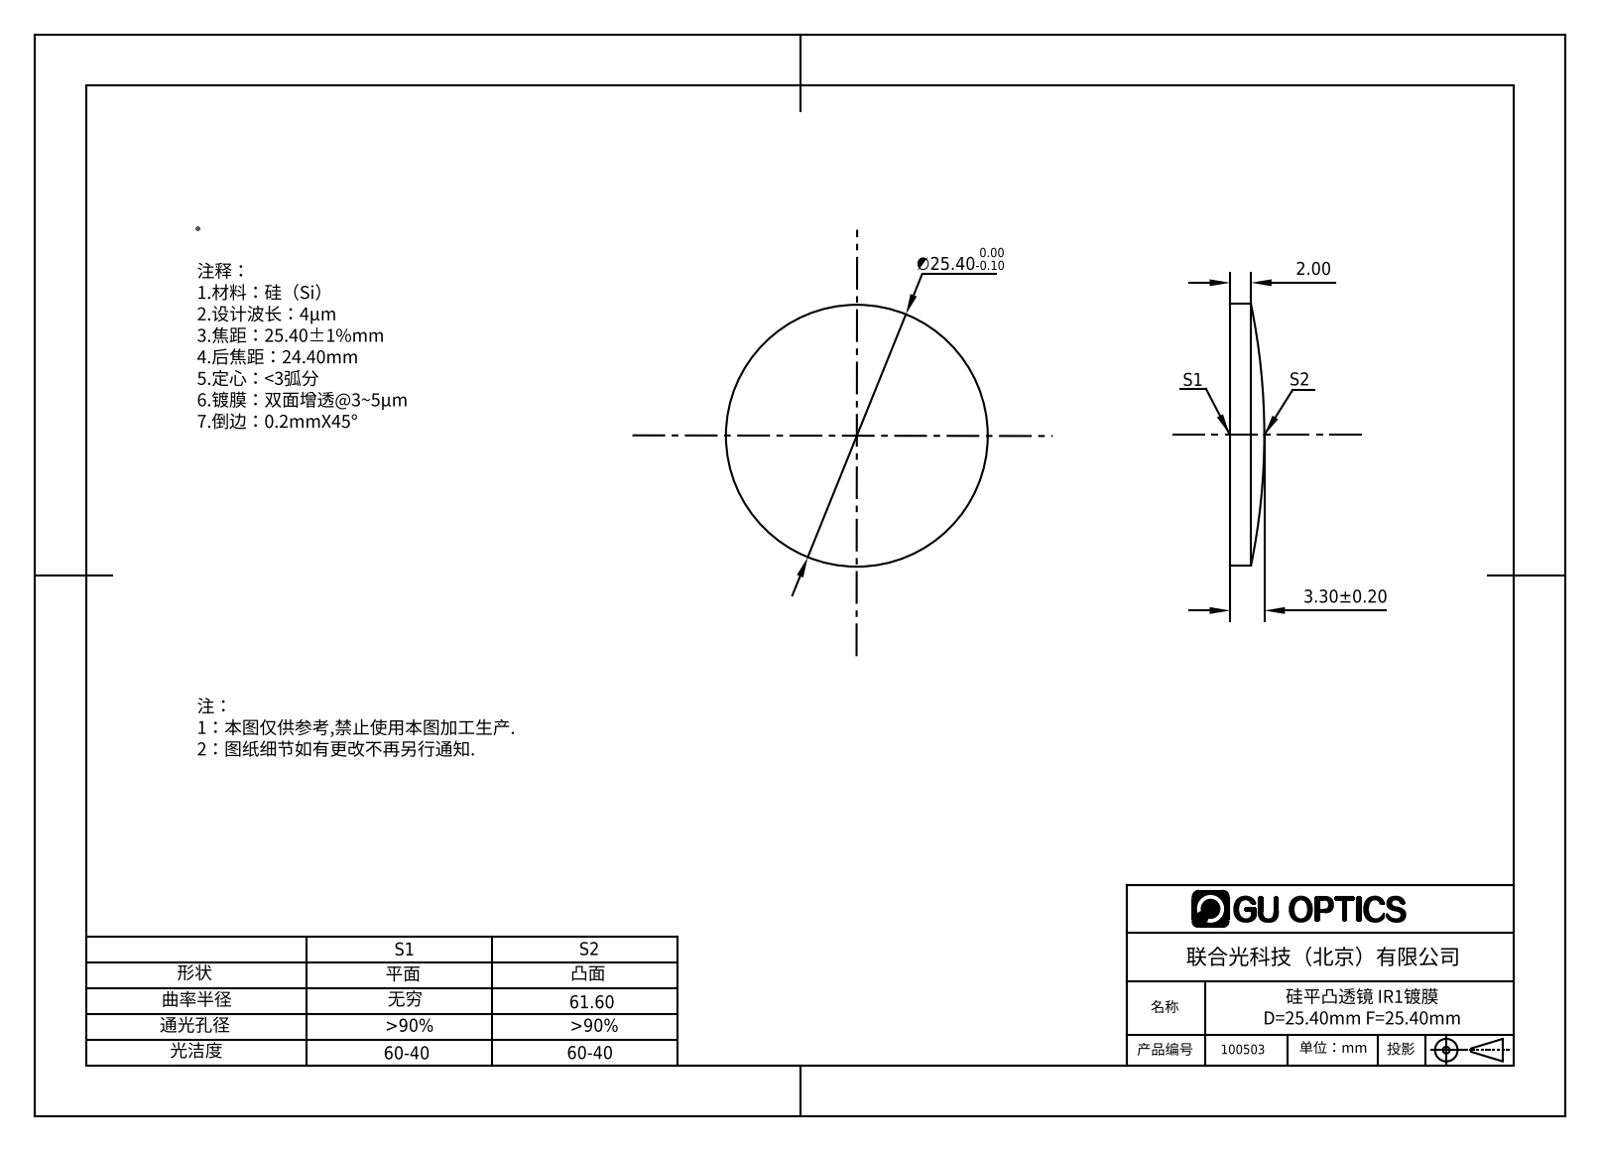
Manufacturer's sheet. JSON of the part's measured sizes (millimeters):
{"part_name": "100491", "step_written_by": "SolidWorks 2016 (AUTOMOTIVE_DESIGN)", "units": "millimeters", "bodies": {"solids": 1, "faces": 5, "planar": 1, "cylindrical": 2, "other": 2}, "overall_size": [25.4, 25.4, 3.3], "volume_mm3": 1344, "surface_area_mm2": 1178, "round_bosses_or_shafts": [[25.4, 1]]}
